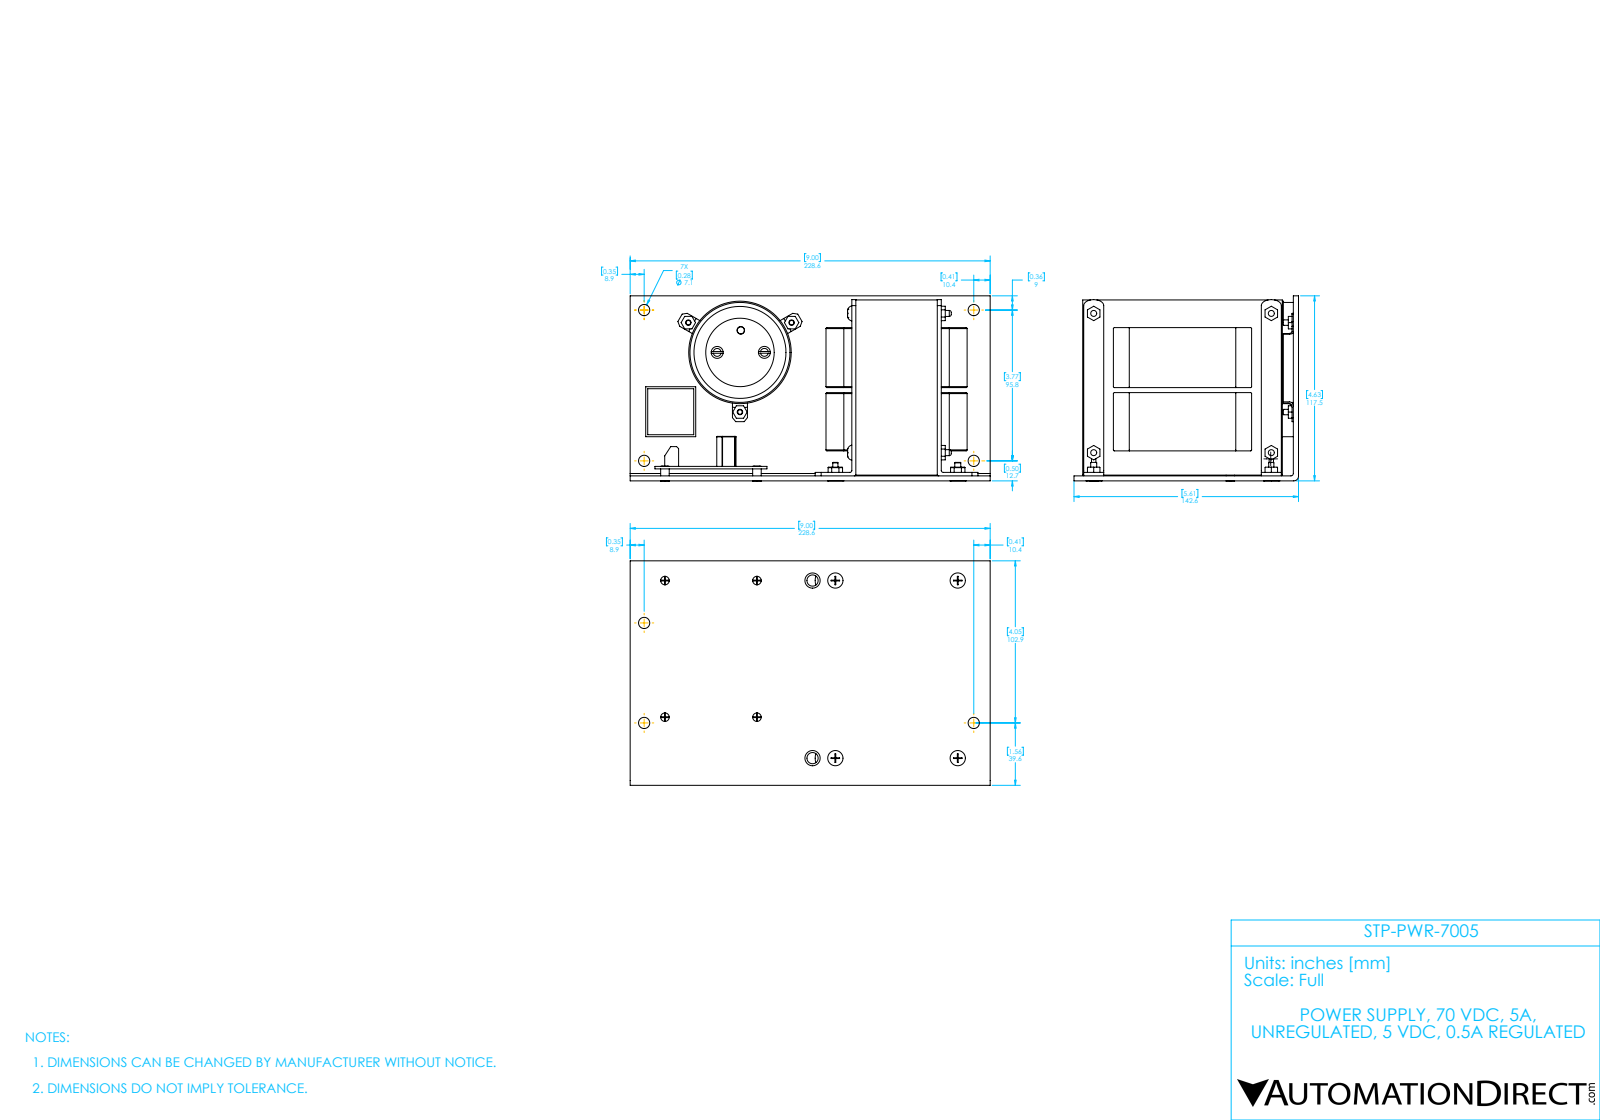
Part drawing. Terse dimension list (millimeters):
name: STP-PWR-7005
written by: SolidWorks 2017 (AUTOMOTIVE_DESIGN)
unit: mm
bodies: 2 solids, 825 faces (472 planar, 251 cylindrical, 102 other)
size: 228.6 × 142.6 × 117.6
volume: 1 562 000 mm³; area: 236 700 mm²
holes: 9× ⌀7.1, 7× ⌀2.7
bosses: 5× ⌀3.8, 4× ⌀9.7, 4× ⌀5.4, 3× ⌀3.5, 3× ⌀3.3, 2× ⌀7.6, 2× ⌀3.1, 2× ⌀2.7
rounds: 22× R0.3, 16× R0.6, 5× R0.3, 4× R1.3, 4× R1.4, 4× R2.7, 4× R2.7, 4× R10.9
face distances: 3.2, 3.3, 19, 70.7, 7.6, 4.4, 3.7, 0.5, 4, 114.9
hole spacings: 6.1, 209.3, 27.9, 29.1, 57.1, 95.8, 230.2, 6.1
